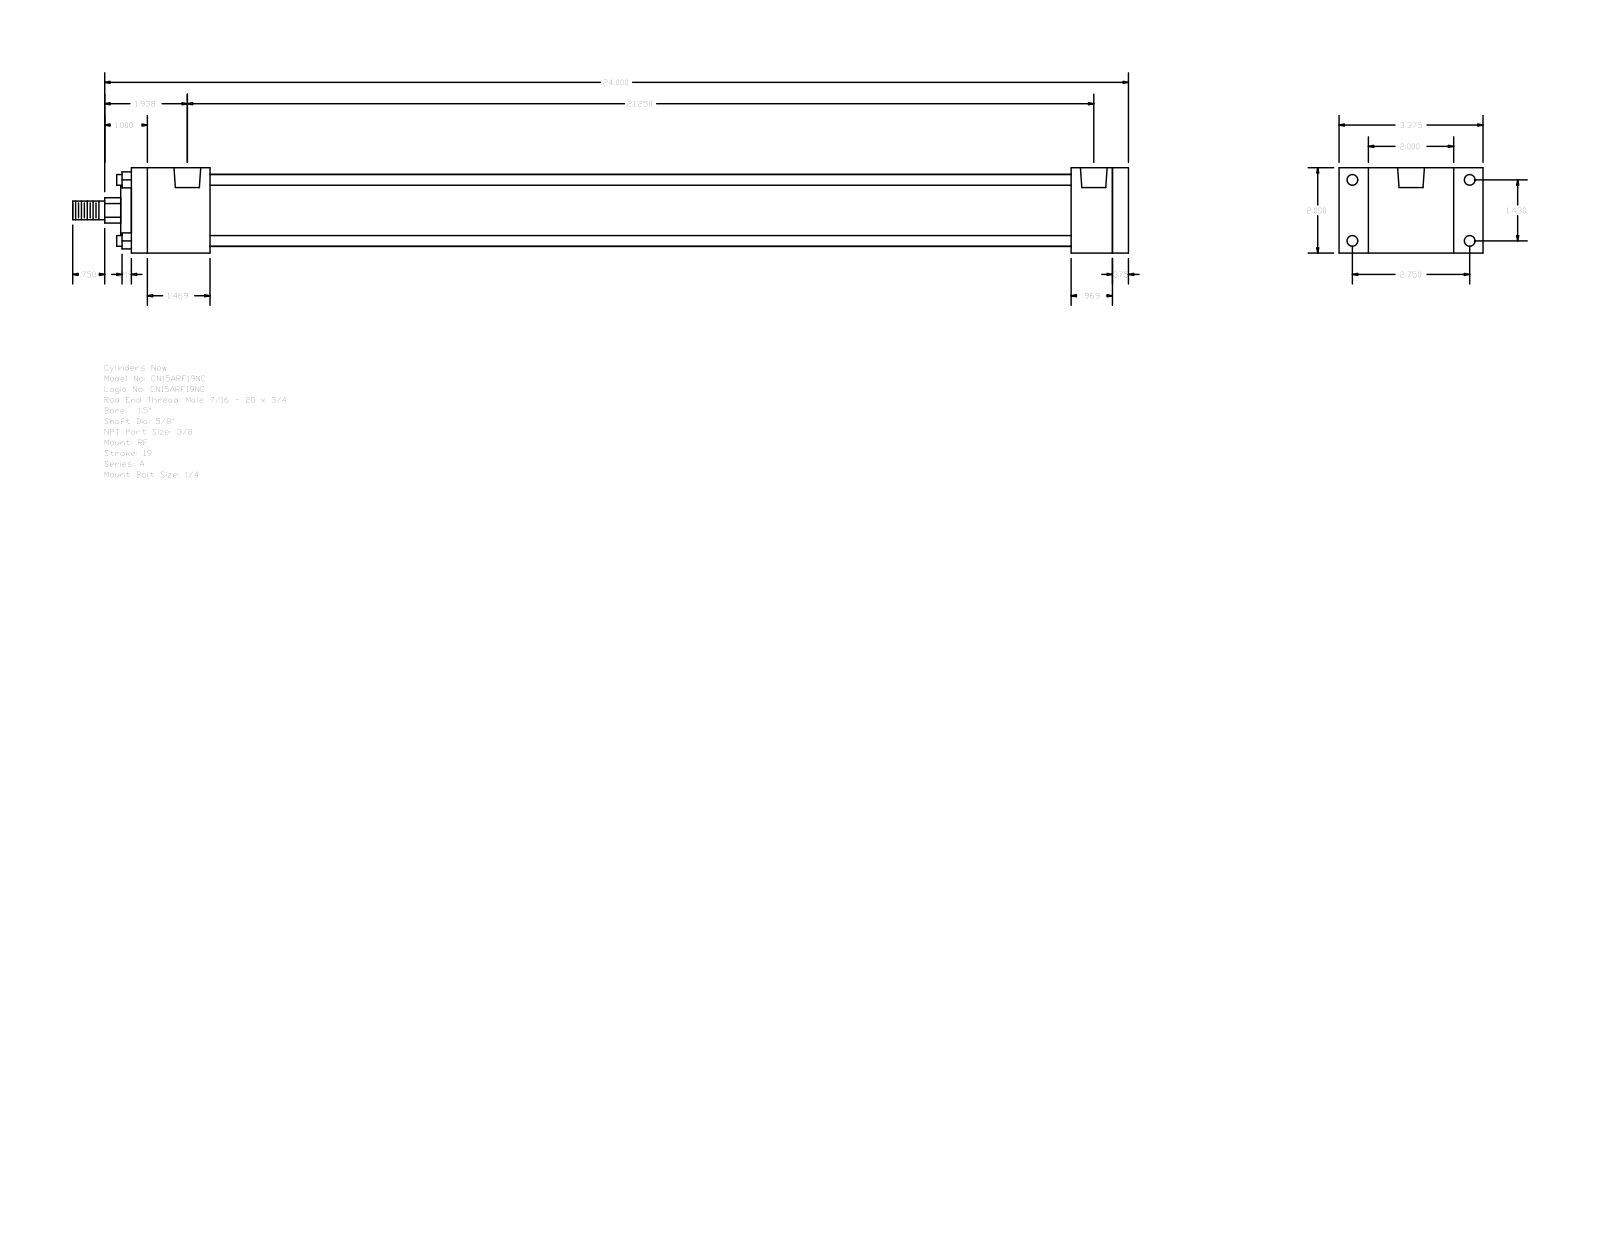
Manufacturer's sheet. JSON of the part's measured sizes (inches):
{"part_name": "A_RF__0150_0.625", "step_written_by": "GSSL Pune (CONFIG_CONTROL_DESIGN)", "units": "inches", "bodies": {"solids": 0, "faces": 92, "planar": 64, "cylindrical": 28, "other": 0}, "overall_size": [24.75, 3.375, 2], "round_holes": [[0.219, 4], [0.25, 4], [0.627, 2]], "round_bosses_or_shafts": [[0.25, 4], [1.69, 1], [1.125, 1], [0.625, 1], [0.437, 1]], "partial_cylinders_radius": [[0.297, 1]], "face_to_face_distances": [2, 0.375, 23, 23.375, 22.031, 0.969, 1.344, 1.844, 20.187, 21.156], "hole_center_spacings": [0.156, 1.43, 2.75, 3.099, 20.937, 21.094, 21.25]}
